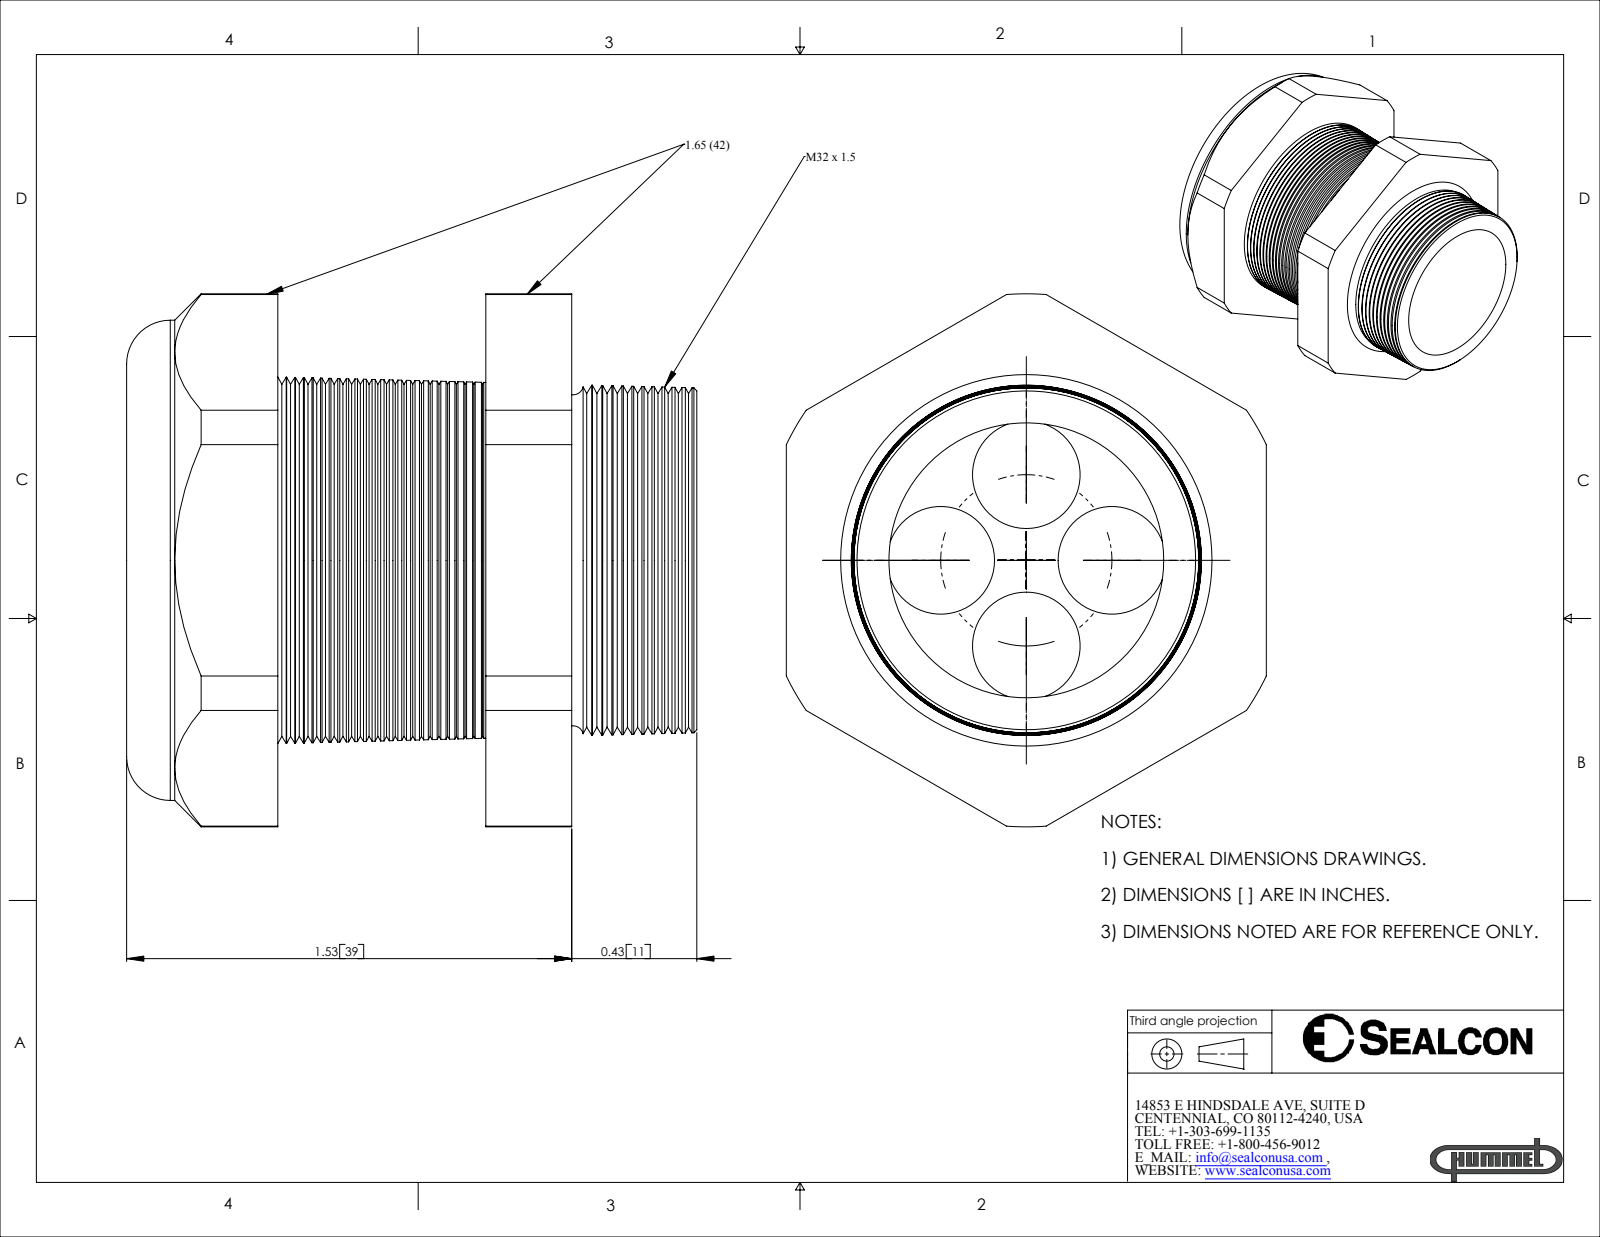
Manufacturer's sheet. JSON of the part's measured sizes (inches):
{"part_name": "CD32M3-BK", "step_written_by": "SolidWorks 2007 (CONFIG_CONTROL_DESIGN)", "units": "inches", "bodies": {"solids": 2, "faces": 279, "planar": 21, "cylindrical": 28, "other": 230}, "overall_size": [1.96, 1.831, 1.65], "volume_in3": 1.87, "surface_area_in2": 27.37, "round_holes": [[0.37, 4], [0.96, 1], [0.98, 1]], "round_bosses_or_shafts": [[1.65, 1]], "partial_cylinders_radius": [[0.916, 1]], "face_to_face_distances": [0.715, 1.011, 0.295, 1.65, 0.52, 1.235, 1.53, 1.65, 1.96, 1.441], "hole_center_spacings": [0.294, 0.416, 0.588]}
